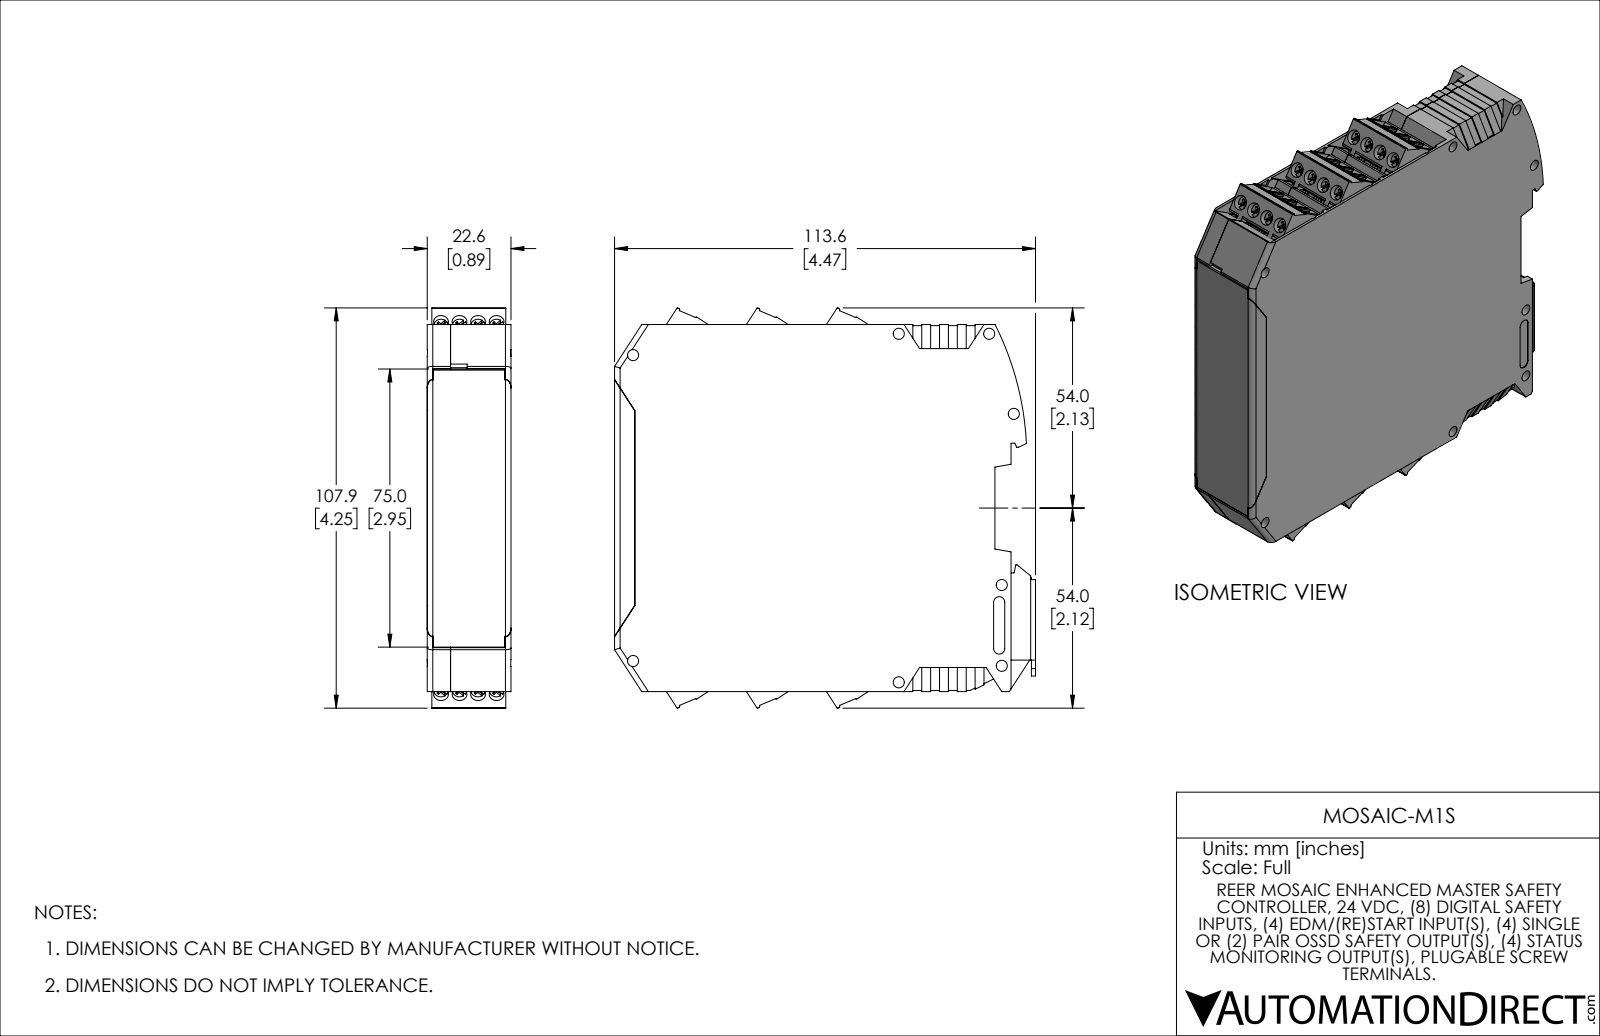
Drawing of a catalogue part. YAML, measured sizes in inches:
part_name: "MOSAIC-M1S"
step_written_by: "SolidWorks 2021 (AUTOMOTIVE_DESIGN)"
units: inches
bodies: {solids: 11, faces: 2255, planar: 1901, cylindrical: 351, other: 3}
overall_size: [4.472, 4.25, 0.89]
volume: 3.801
surface_area: 126.7
round_holes:
  - {diameter: 0.055, count: 26}
  - {diameter: 0.11, count: 24}
  - {diameter: 0.157, count: 24}
  - {diameter: 0.118, count: 14}
  - {diameter: 0.063, count: 1}
round_bosses_or_shafts:
  - {diameter: 0.149, count: 24}
  - {diameter: 0.177, count: 1}
  - {diameter: 0.11, count: 1}
  - {diameter: 0.053, count: 1}
partial_cylinders:
  - {radius: 0.012, count: 49}
  - {radius: 0.114, count: 24}
  - {radius: 0.008, count: 18}
  - {radius: 0.03, count: 18}
  - {radius: 0.059, count: 10}
  - {radius: 0.024, count: 6}
  - {radius: 0.039, count: 6}
  - {radius: 0.098, count: 5}
face_to_face_distances: [0.049, 0.841, 0.89, 0.791, 0.713, 0.197, 0.039, 0.248, 0.047, 0.593]
hole_center_spacings: [0.197, 0.394, 0.503, 0.504, 0.591, 0.739, 0.74, 0.947]
